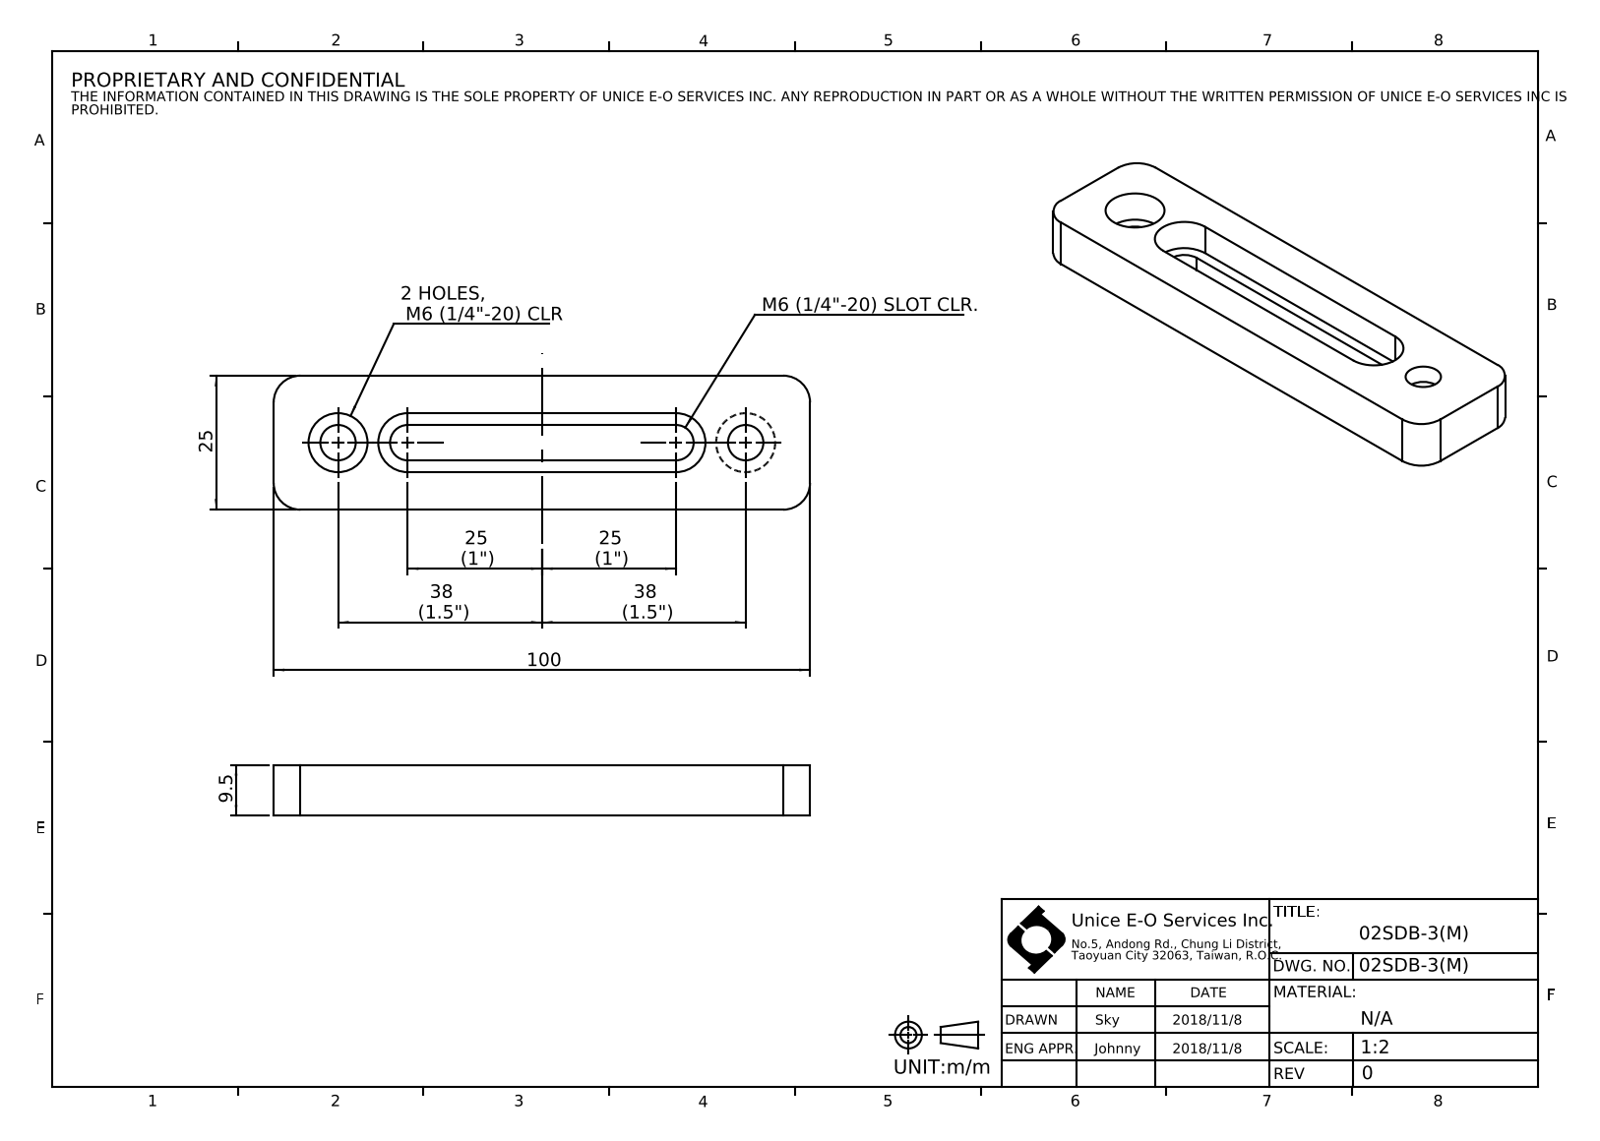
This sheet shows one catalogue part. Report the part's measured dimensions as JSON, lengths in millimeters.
{"part_name": "02SDB-3(M)", "step_written_by": "SolidWorks 2016 (AUTOMOTIVE_DESIGN)", "units": "millimeters", "bodies": {"solids": 1, "faces": 29, "planar": 13, "cylindrical": 16, "other": 0}, "overall_size": [100, 25, 9.5], "volume_mm3": 17021, "surface_area_mm2": 8175, "round_holes": [[6.6, 2], [11, 2]], "partial_cylinders_radius": [[5, 4], [3.3, 2], [5.5, 2]], "face_to_face_distances": [9.5, 25, 7, 18, 3.5, 6, 9.2, 15.8, 2.2, 8.8], "hole_center_spacings": [76]}
